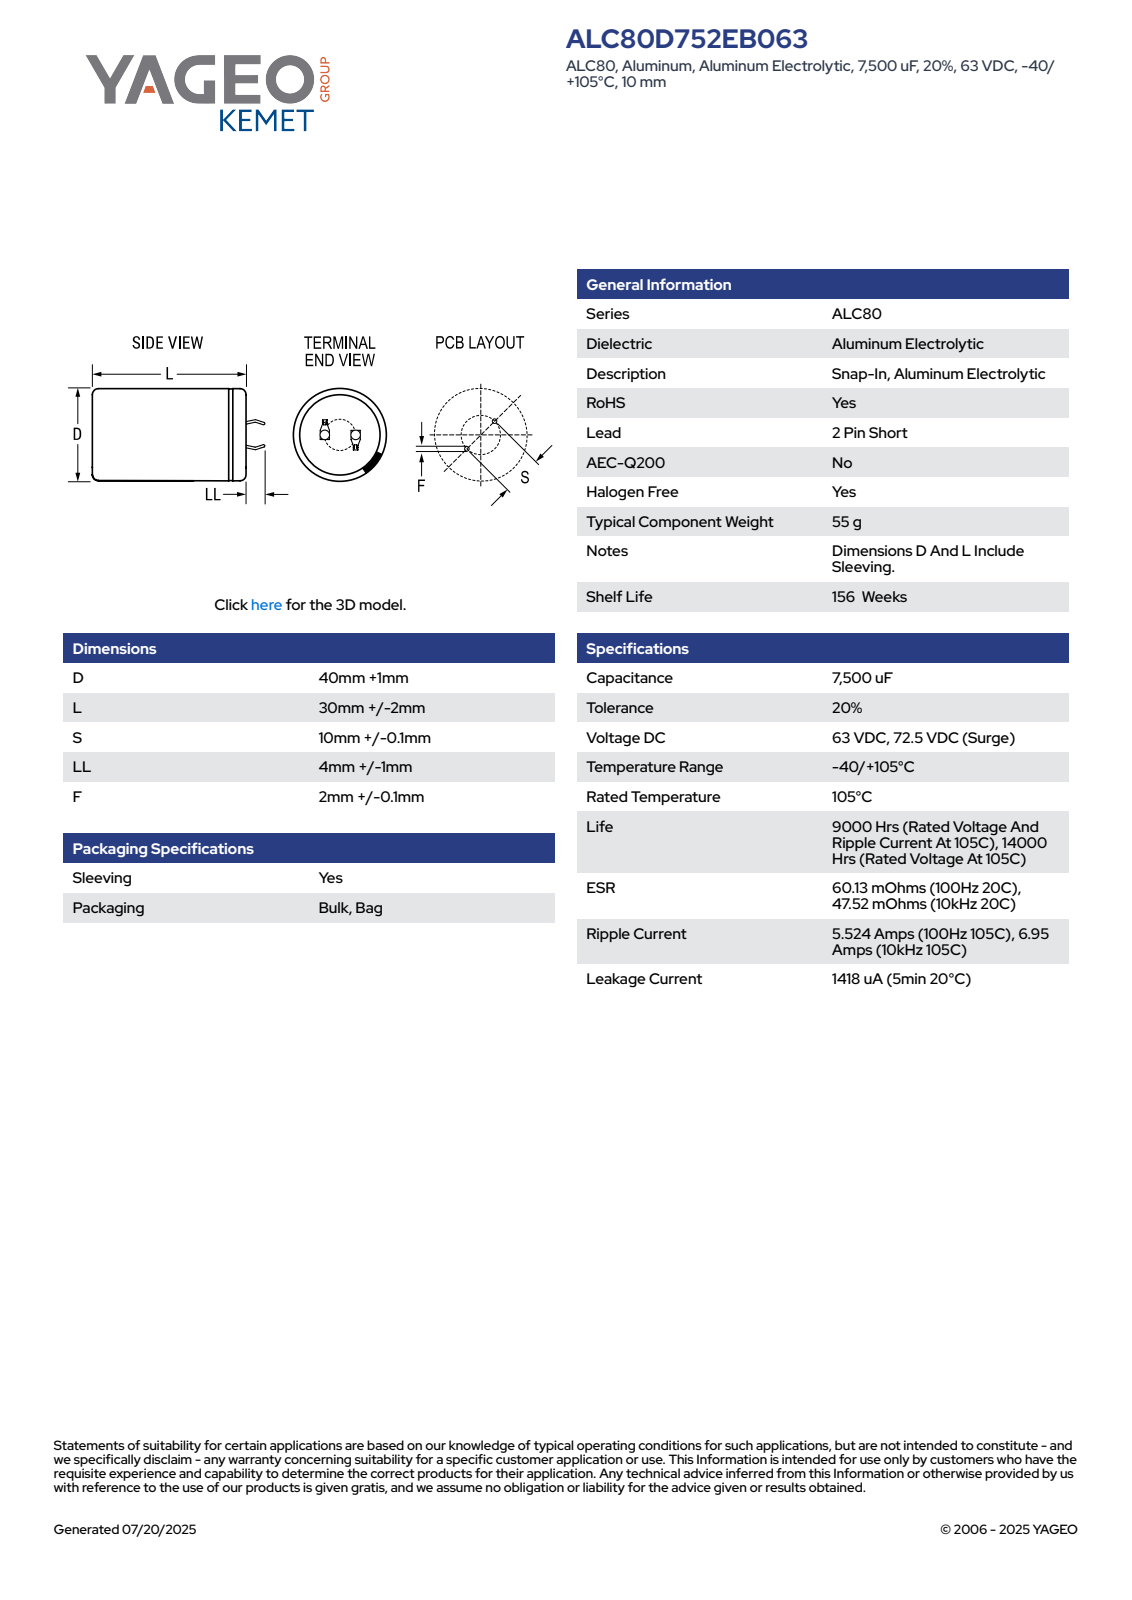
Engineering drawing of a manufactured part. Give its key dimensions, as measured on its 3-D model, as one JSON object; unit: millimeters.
{"part_name": "CARS_K2P_40X30_D41L32S10LL5F2.1", "step_written_by": "SolidWorks 2014 (AUTOMOTIVE_DESIGN)", "units": "millimeters", "bodies": {"solids": 1, "faces": 100, "planar": 52, "cylindrical": 9, "other": 39}, "overall_size": [41, 41, 36.99], "volume_mm3": 41462, "surface_area_mm2": 6734, "round_holes": [[36.28, 1]], "round_bosses_or_shafts": [[41, 1]], "partial_cylinders_radius": [[20.49, 1]], "face_to_face_distances": [31.99, 32.49, 0.5, 7.08, 0.6, 0.59, 7.6, 0.75, 1.35, 7.68]}
